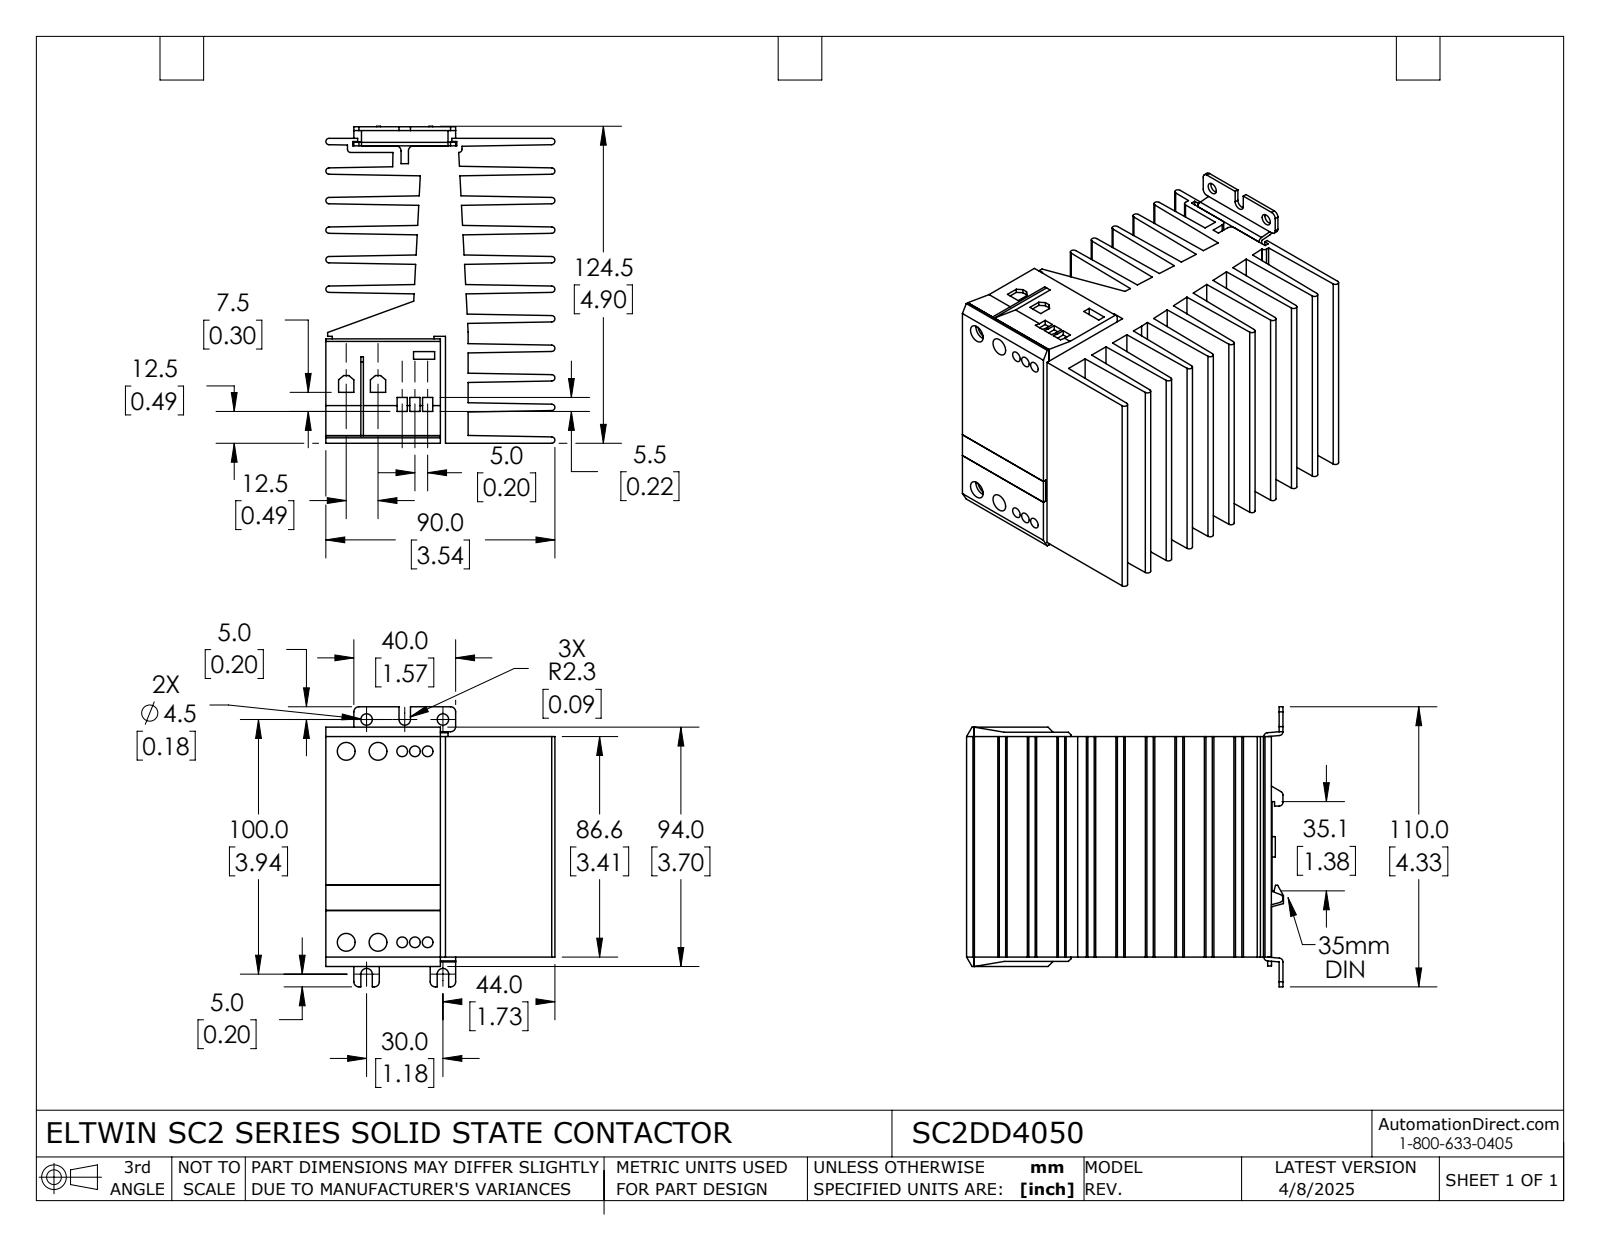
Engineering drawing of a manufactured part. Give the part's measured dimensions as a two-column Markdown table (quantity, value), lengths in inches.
| quantity | value |
| --- | --- |
| part name | SC2DD4050 |
| STEP written by | SolidWorks 2021 (AUTOMOTIVE_DESIGN) |
| units | inches |
| bodies | 7 solids, 404 faces (294 planar, 110 cylindrical, 0 other) |
| overall size | 4.902 × 4.331 × 3.543 |
| volume | 31.2 in³ |
| surface area | 277.4 in² |
| round holes (diameter × count) | 0.165 × 6, 0.173 × 6, 0.276 × 4, 0.177 × 2, 0.315 × 2 |
| round bosses / shafts (diameter × count) | 0.315 × 3 |
| partial cylindrical surfaces (radius × count) | 0.049 × 19, 0.079 × 18, 0.059 × 10, 0.051 × 4, 0.089 × 3 |
| main face-to-face distances | 0.457, 0.913, 1.37, 0.159, 0.3, 0.157, 1.827, 1.669, 1.828, 2.126 |
| hole center spacings | 2.953, 0.197, 2.959, 0.374, 0.394, 0.492, 0.571, 0.768 |
